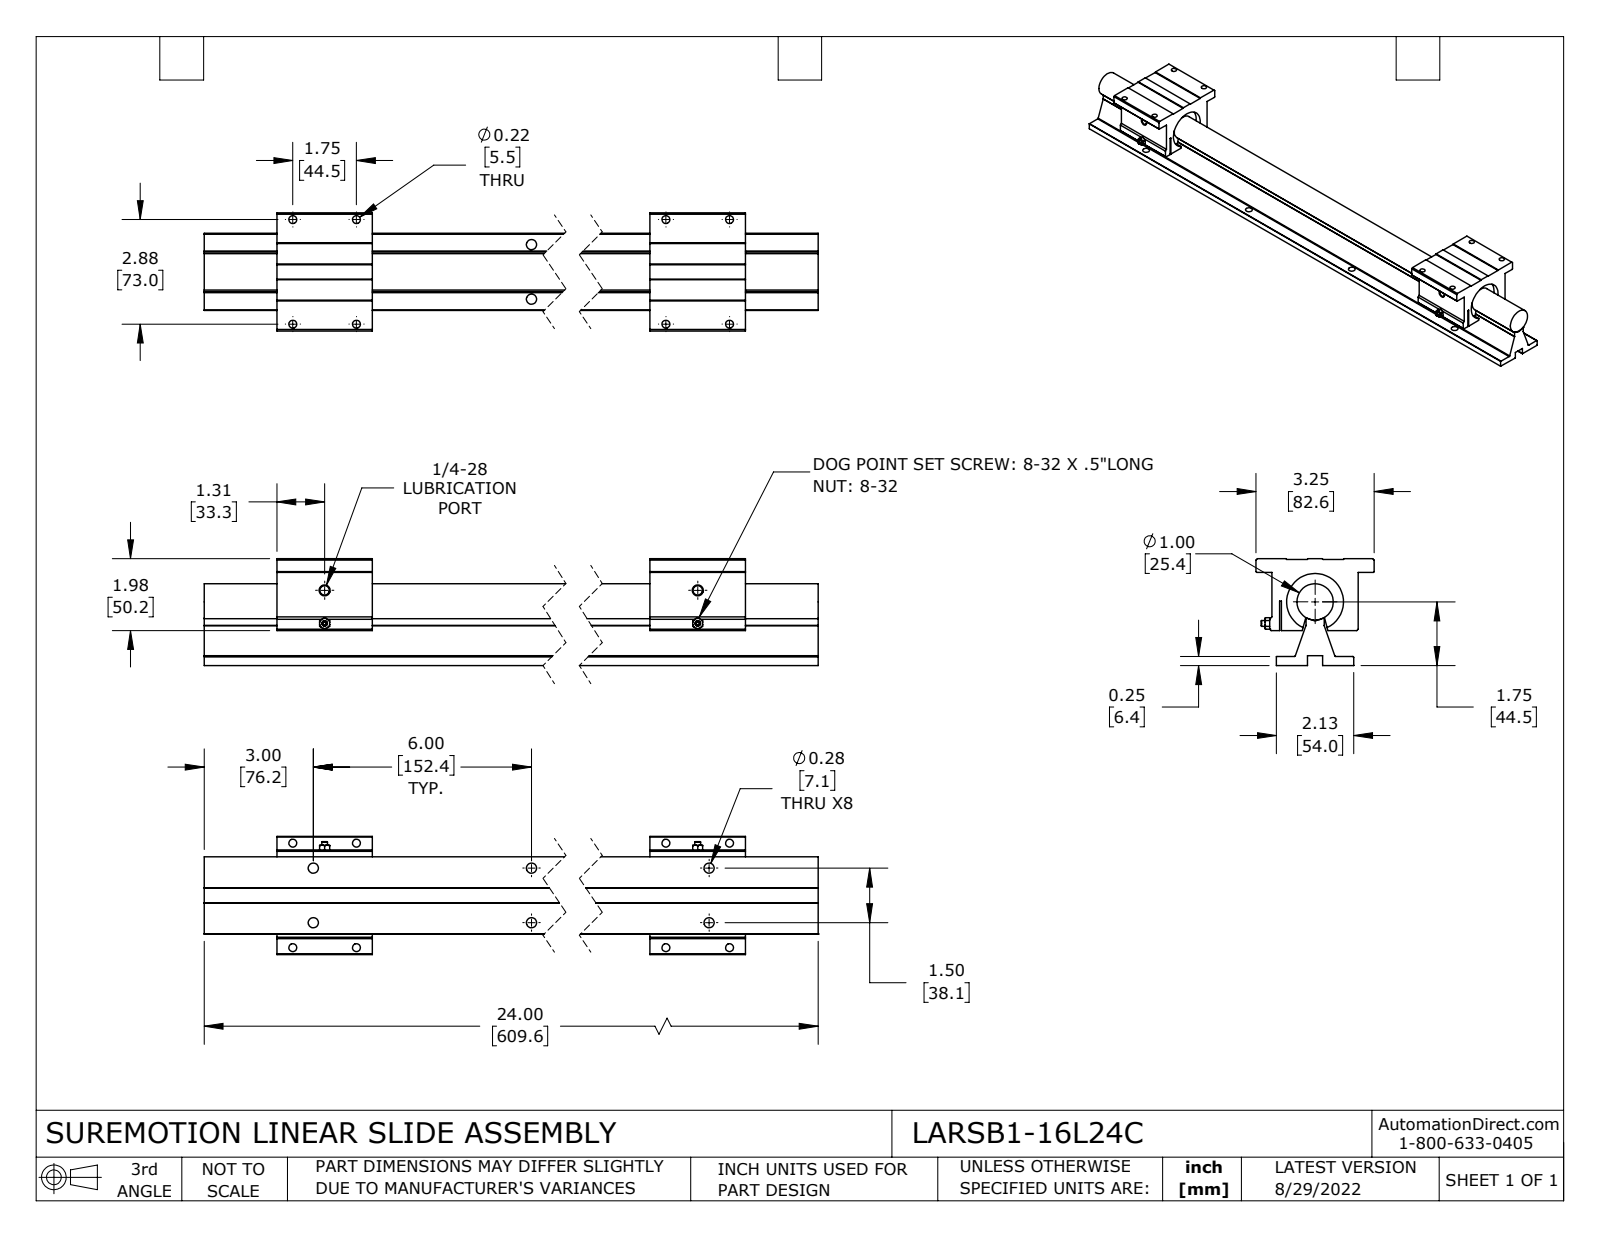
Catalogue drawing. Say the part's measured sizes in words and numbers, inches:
The part is named "LARSB1-16L24C-RAIL; LARSACC-006; LARSB1-16L24C". Its 3-D file was written by "SolidWorks 2021 (CONFIG_CONTROL_DESIGN)". It is 6 solids with 215 faces: 121 planar, 74 cylindrical and 20 other. Overall it measures 24 by 3.25 by 2.937 inches. Its volume is 67.1 cubic inches and its surface area 342.6 square inches. Round holes: 8 of diameter 0.218, 8 of diameter 0.281, 2 of diameter 0.258, 1 of diameter 1, 1 of diameter 1.562. Round bosses or shafts: 2 of diameter 0.157. Partial cylindrical surfaces (rounded edges, fillets, slot ends): 11 of radius 0.03, 1 of radius 0.075, 1 of radius 0.499. The main face-to-face distances are 0.25, 0.981, 1.396, 0.126, 2.251, 0.855, 1.27, 2.937, 2.687, 0.27. The hole center spacings are 6, 6.185, 0.888, 1.372, 1.5, 1.75, 2.259, 2.489.
